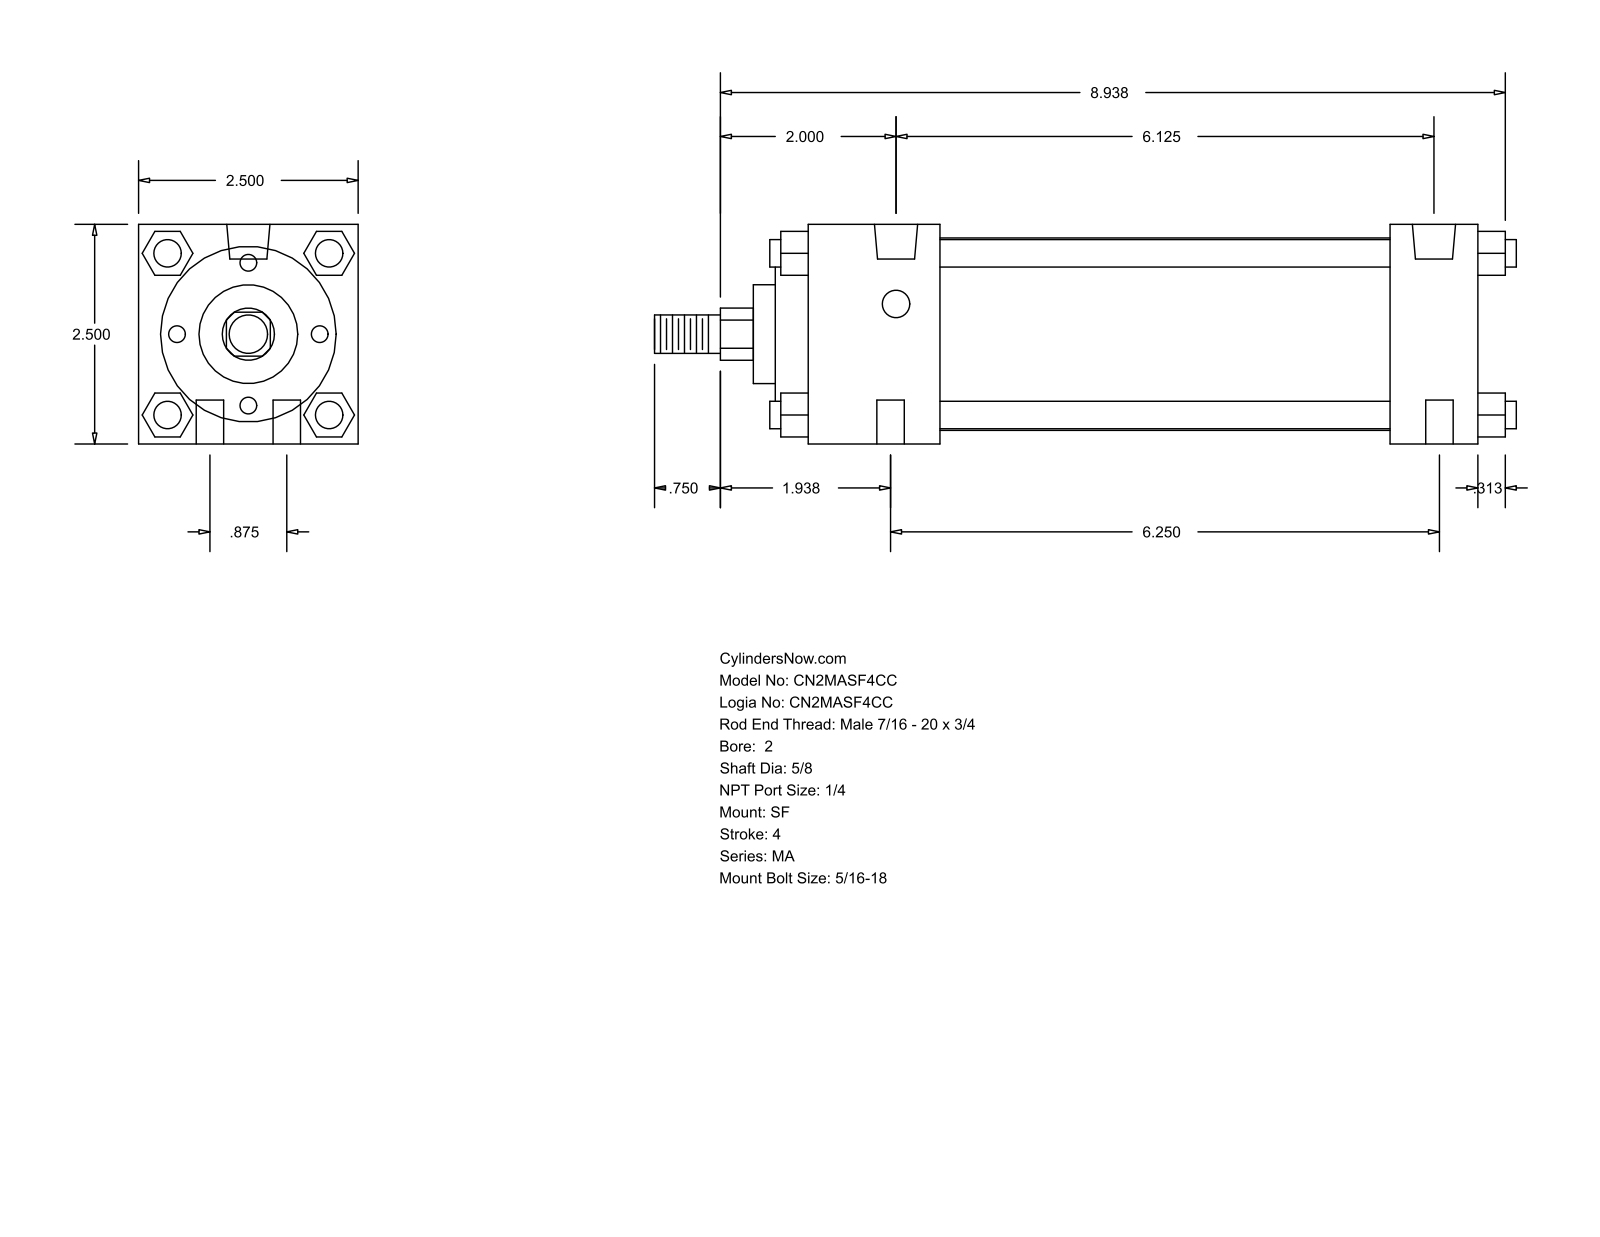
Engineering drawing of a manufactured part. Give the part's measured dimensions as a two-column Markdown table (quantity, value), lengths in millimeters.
| quantity | value |
| --- | --- |
| part name | MA_SF__0200_0.625 |
| STEP written by | GSSL Pune (CONFIG_CONTROL_DESIGN) |
| units | millimeters |
| bodies | 0 solids, 126 faces (95 planar, 31 cylindrical, 0 other) |
| overall size | 249.24 × 63.5 × 63.5 |
| round holes (diameter × count) | 7.94 × 6, 12.49 × 2 |
| round bosses / shafts (diameter × count) | 7.94 × 4, 55.63 × 1, 50.8 × 1, 28.57 × 1, 15.88 × 1, 11.11 × 1 |
| partial cylindrical surfaces (radius × count) | 7.54 × 1 |
| main face-to-face distances | 63.5, 12.7, 38.1, 193.67, 168.28, 25.39, 130.18, 155.57, 9.52, 47.62 |
| hole center spacings | 11.22, 22.22, 155.58, 157.55, 157.56, 158.75, 160.3 |
